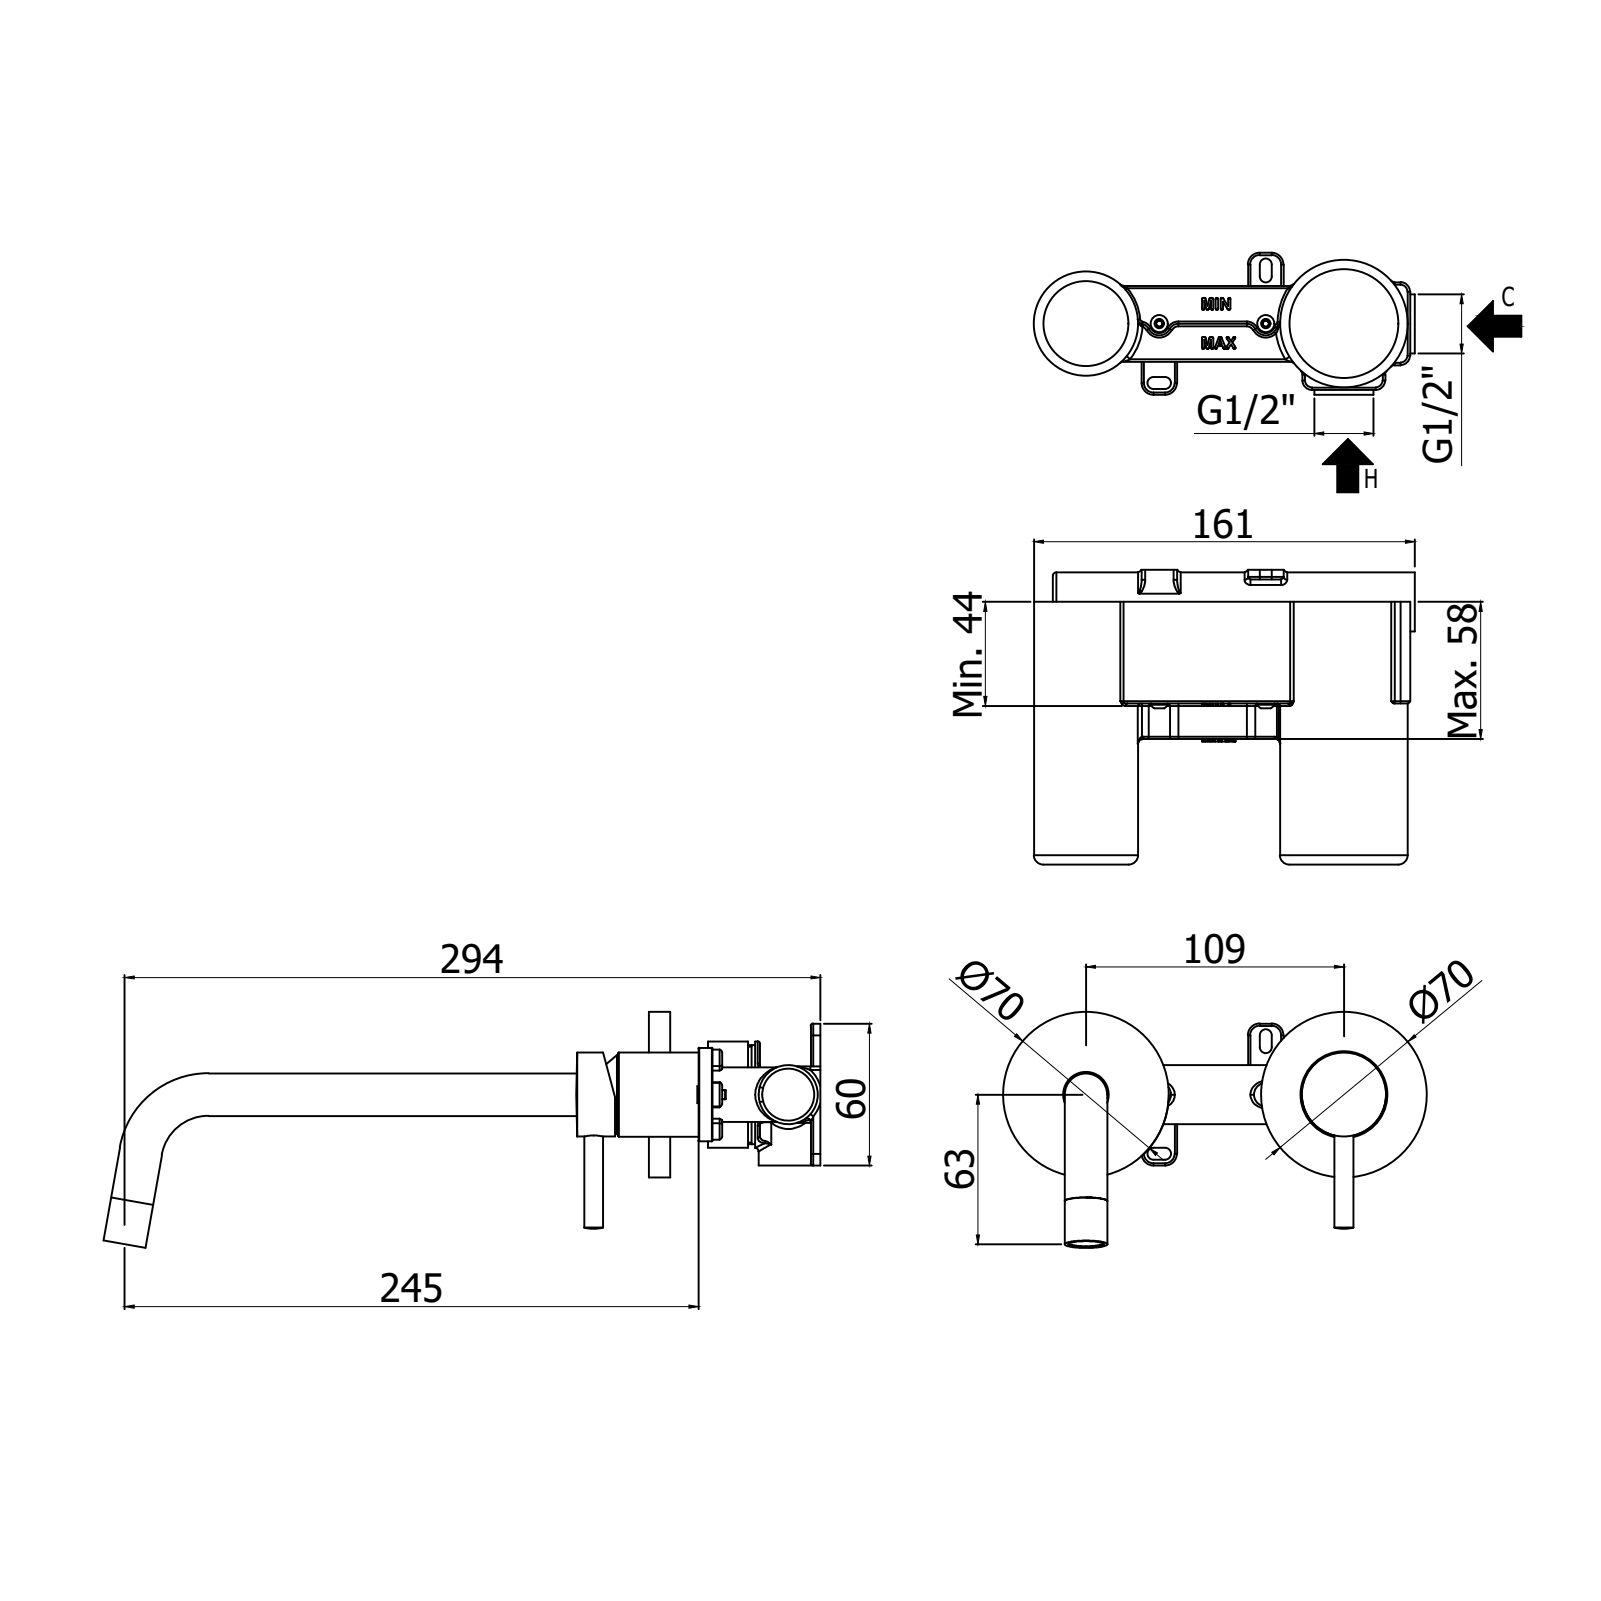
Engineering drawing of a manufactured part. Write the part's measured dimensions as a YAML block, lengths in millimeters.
part_name: "LIG103CR70"
step_written_by: "CREO PARAMETRIC BY PTC INC, 2020044 (CONFIG_CONTROL_DESIGN)"
units: millimeters
bodies: {solids: 4, faces: 85, planar: 30, cylindrical: 33, other: 22}
overall_size: [244.38, 179, 99.78]
volume: 148877
surface_area: 48755
round_holes:
  - {diameter: 5.6, count: 1}
  - {diameter: 22.5, count: 1}
  - {diameter: 25.5, count: 1}
  - {diameter: 30, count: 1}
  - {diameter: 31.5, count: 1}
round_bosses_or_shafts:
  - {diameter: 70, count: 2}
  - {diameter: 35.5, count: 2}
  - {diameter: 18, count: 2}
  - {diameter: 33.5, count: 1}
  - {diameter: 8, count: 1}
partial_cylinders:
  - {radius: 2.5, count: 1}
  - {radius: 8.3, count: 1}
face_to_face_distances: [9, 8.93, 8.86, 32.43, 23.5, 37.8, 37.73, 28.87, 28.8, 32.36]
